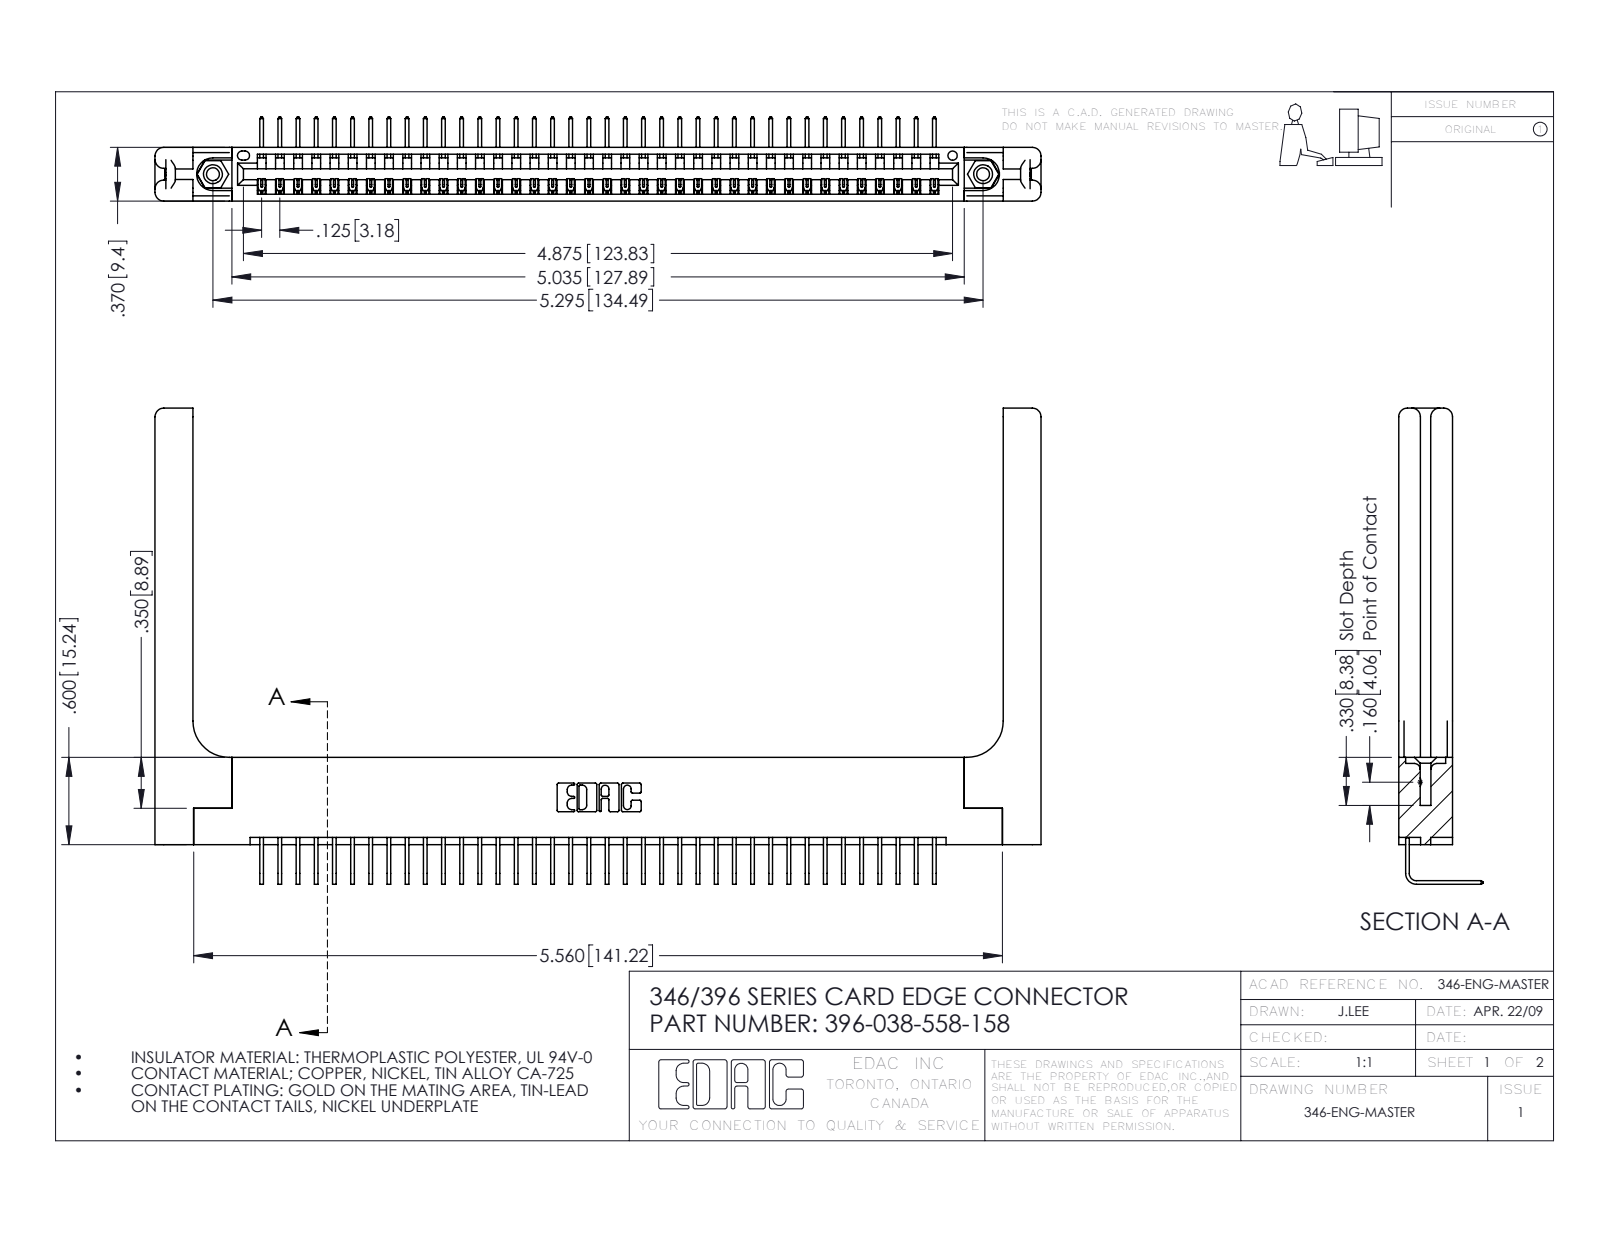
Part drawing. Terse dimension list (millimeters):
name: 346 Part_Flush Mounting Lugs - 0.156 Dia-TH; 345-250-001_345-250-001-102; 396-038-558-158; 346-220-058_345-220-058 (+1 more)
written by: SolidWorks 2016 (CONFIG_CONTROL_DESIGN)
unit: mm
bodies: 43 solids, 2658 faces (1820 planar, 778 cylindrical, 60 other)
size: 154.7 × 83.1 × 14.7
volume: 22 430 mm³; area: 24 520 mm²
holes: 2× ⌀2.3, 2× ⌀3.2, 2× ⌀4, 1× ⌀1.6
bosses: 2× ⌀3.9
rounds: 76× R0.2, 22× R0.3, 16× R1.5, 6× R0.2, 6× R0.8, 3× R0.7, 2× R0.8, 2× R0.8
face distances: 9.4, 8.2, 1.2, 1.8, 3.8, 3.8, 0.6, 6.4, 7.6, 5.6
hole spacings: 6.2, 129.2, 134.5
